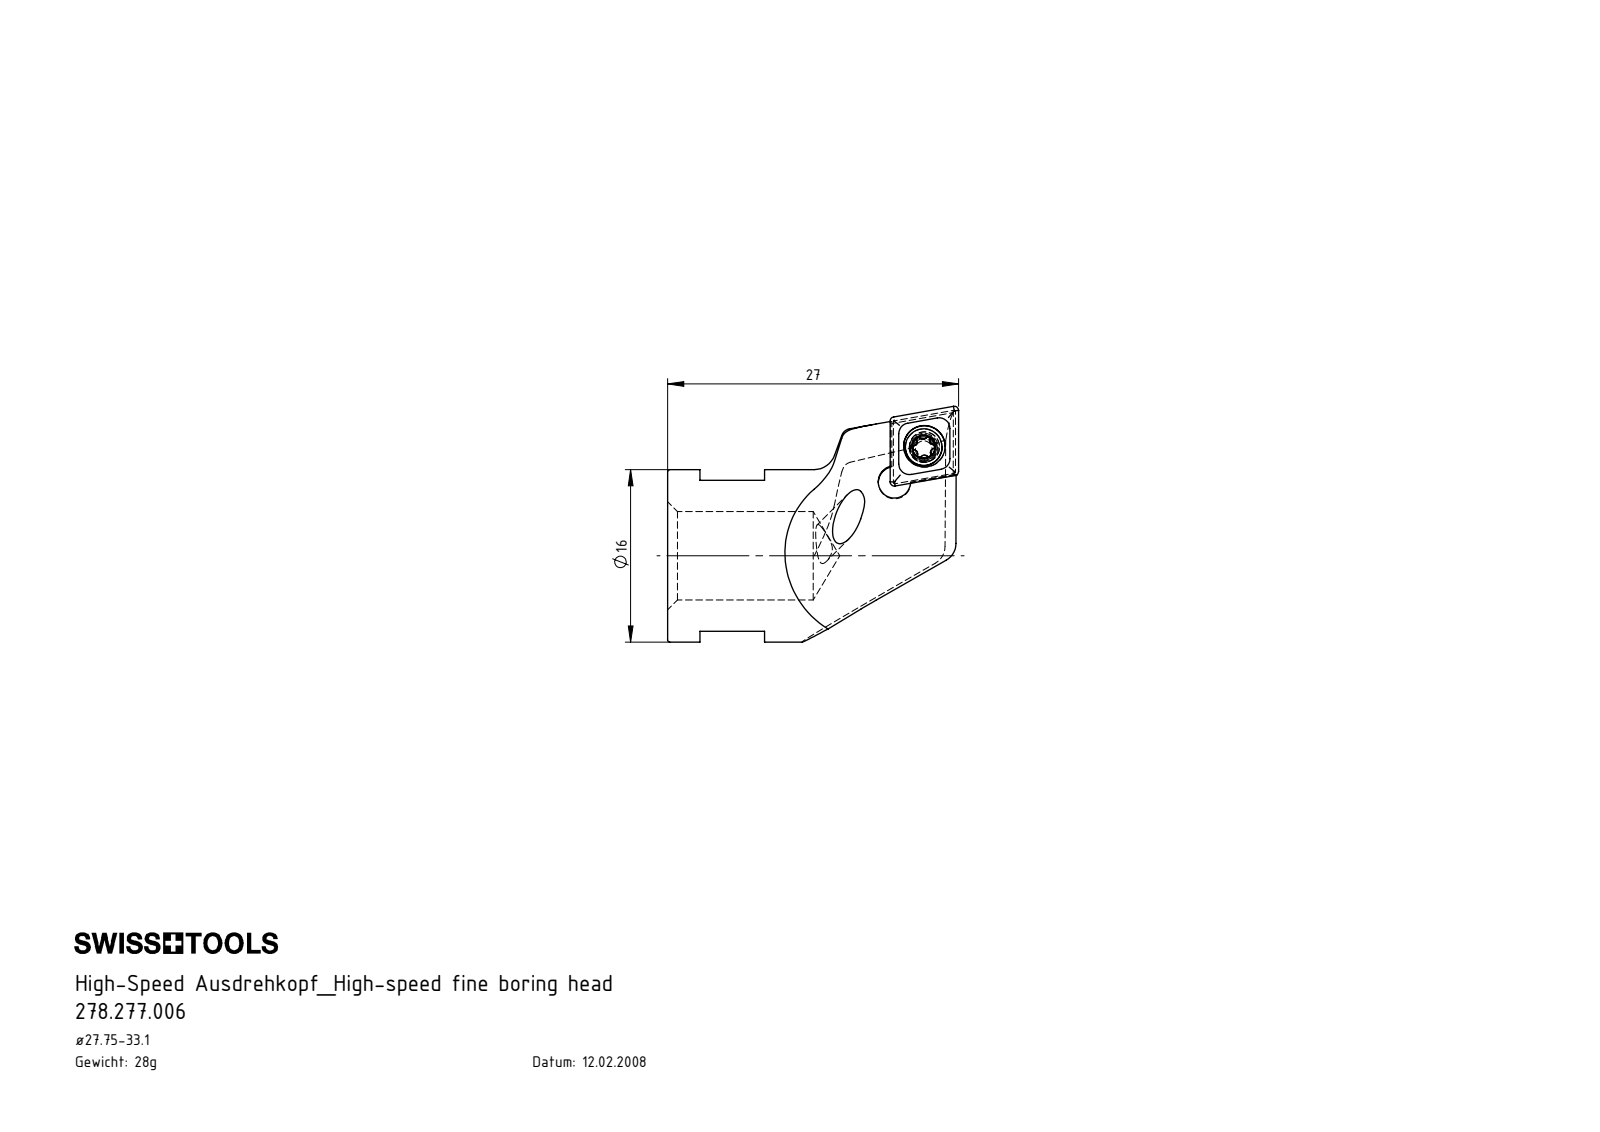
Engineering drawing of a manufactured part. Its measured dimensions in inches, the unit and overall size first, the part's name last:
Units: inches
Overall size (bounding box): 1.063 × 0.861 × 0.63
Round holes (diameter × count): ⌀0.081 ×1, ⌀0.11 ×1, ⌀0.118 ×1, ⌀0.152 ×1, ⌀0.323 ×1
Round bosses / shafts (diameter × count): ⌀0.63 ×1, ⌀0.134 ×1, ⌀0.098 ×1
Partial cylindrical surfaces — rounded edges, fillets, slot ends (radius × count): R0.008 ×6, R0.014 ×5, R0.039 ×4, R0.014 ×1, R0.059 ×1, R0.071 ×1, R0.079 ×1
Main face-to-face distances: 0.09, 0.551, 0.118, 0.354, 0.236, 0.094, 0.098, 0.102, 0.819, 0.701
Volume: 0.214 in³ · Surface area: 3.5 in²
Bodies: 3 solids, 133 faces (39 planar, 40 cylindrical, 54 other)
Part name (STEP PRODUCT): HS0-A28.K11.027; CCMT060204; HS0-A28.K11.027_A; WCA-ER2.001.006_A
STEP written by: SolidWorks 2015 (CONFIG_CONTROL_DESIGN)
